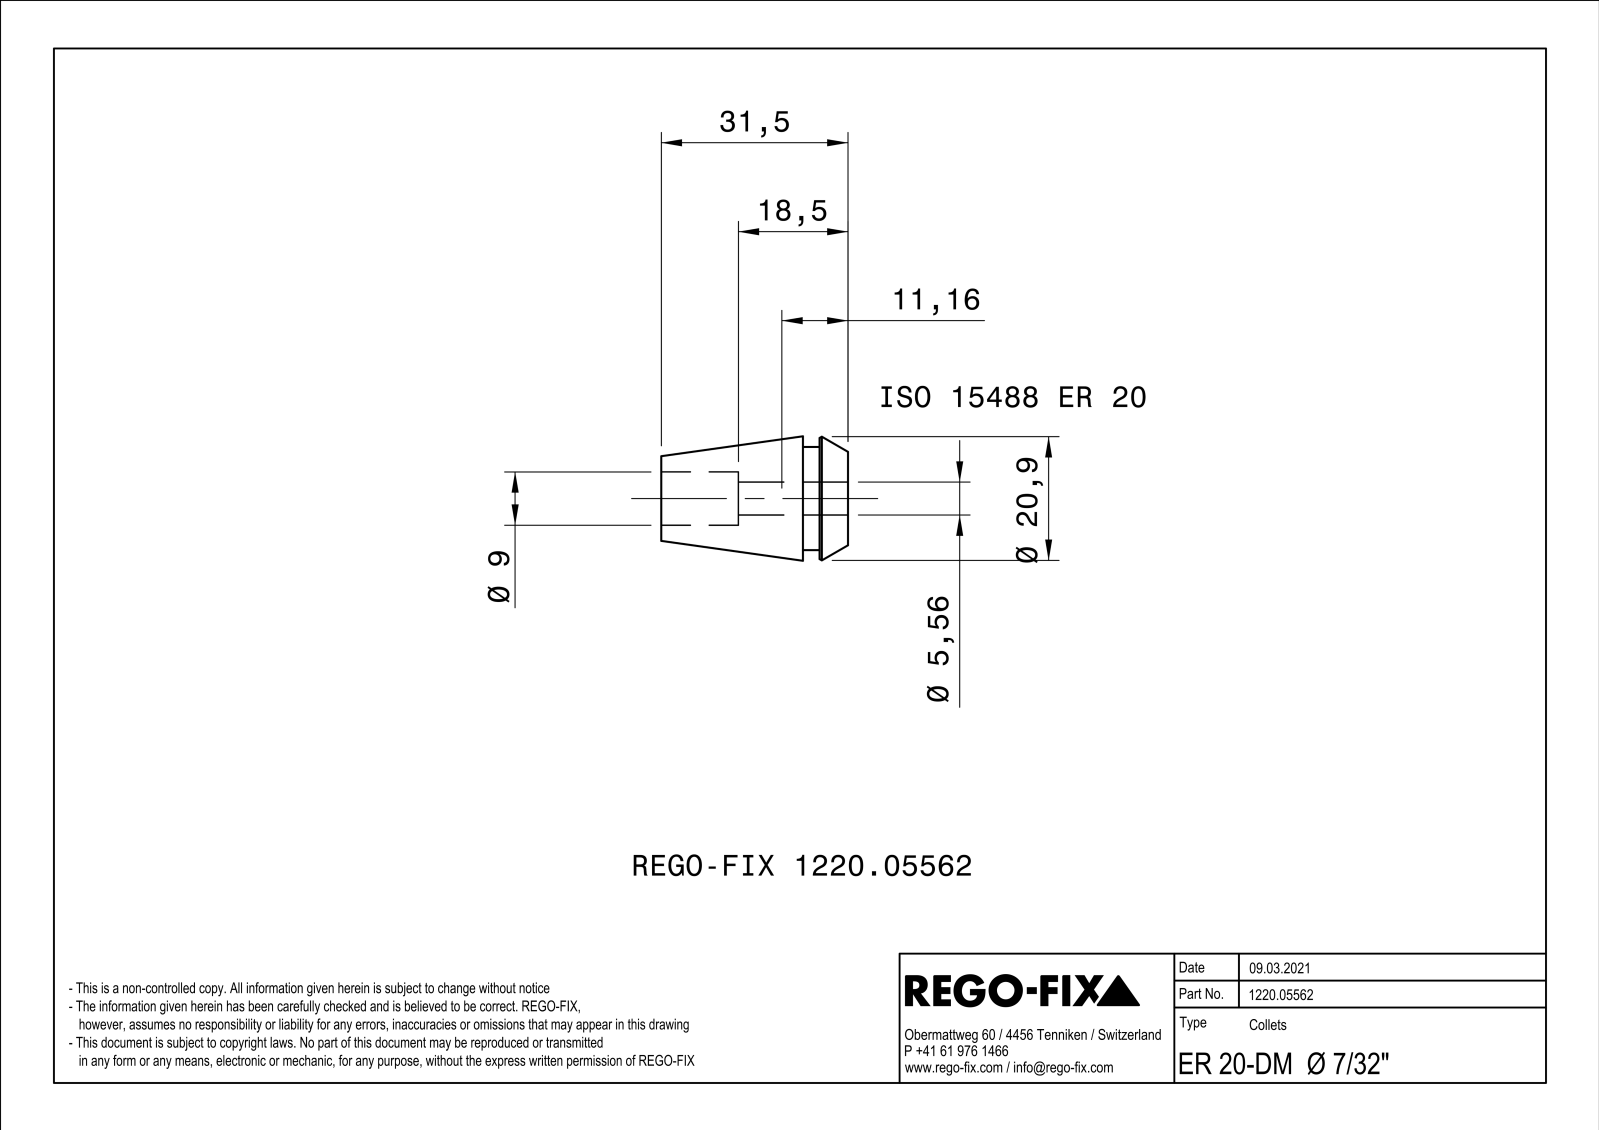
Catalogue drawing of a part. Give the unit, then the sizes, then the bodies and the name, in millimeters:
Units: millimetres
Overall size (bounding box): 31.5 × 20.6 × 20.6
Round holes (diameter × count): ⌀5.56 ×1, ⌀9 ×1
Round bosses / shafts (diameter × count): ⌀17.4 ×1
Main face-to-face distances: 0.6, 7.6, 4.8, 2.8, 31.5, 26.7, 23.9, 18.5, 13.7, 10.9
Volume: 5 473 mm³ · Surface area: 4 220 mm²
Bodies: 1 solid, 94 faces (44 planar, 9 cylindrical, 41 other)
Part name (STEP PRODUCT): NOCUT
STEP written by: SIEMENS PLM Software Solid Edge ST10 (AUTOMOTIVE_DESIGN)
